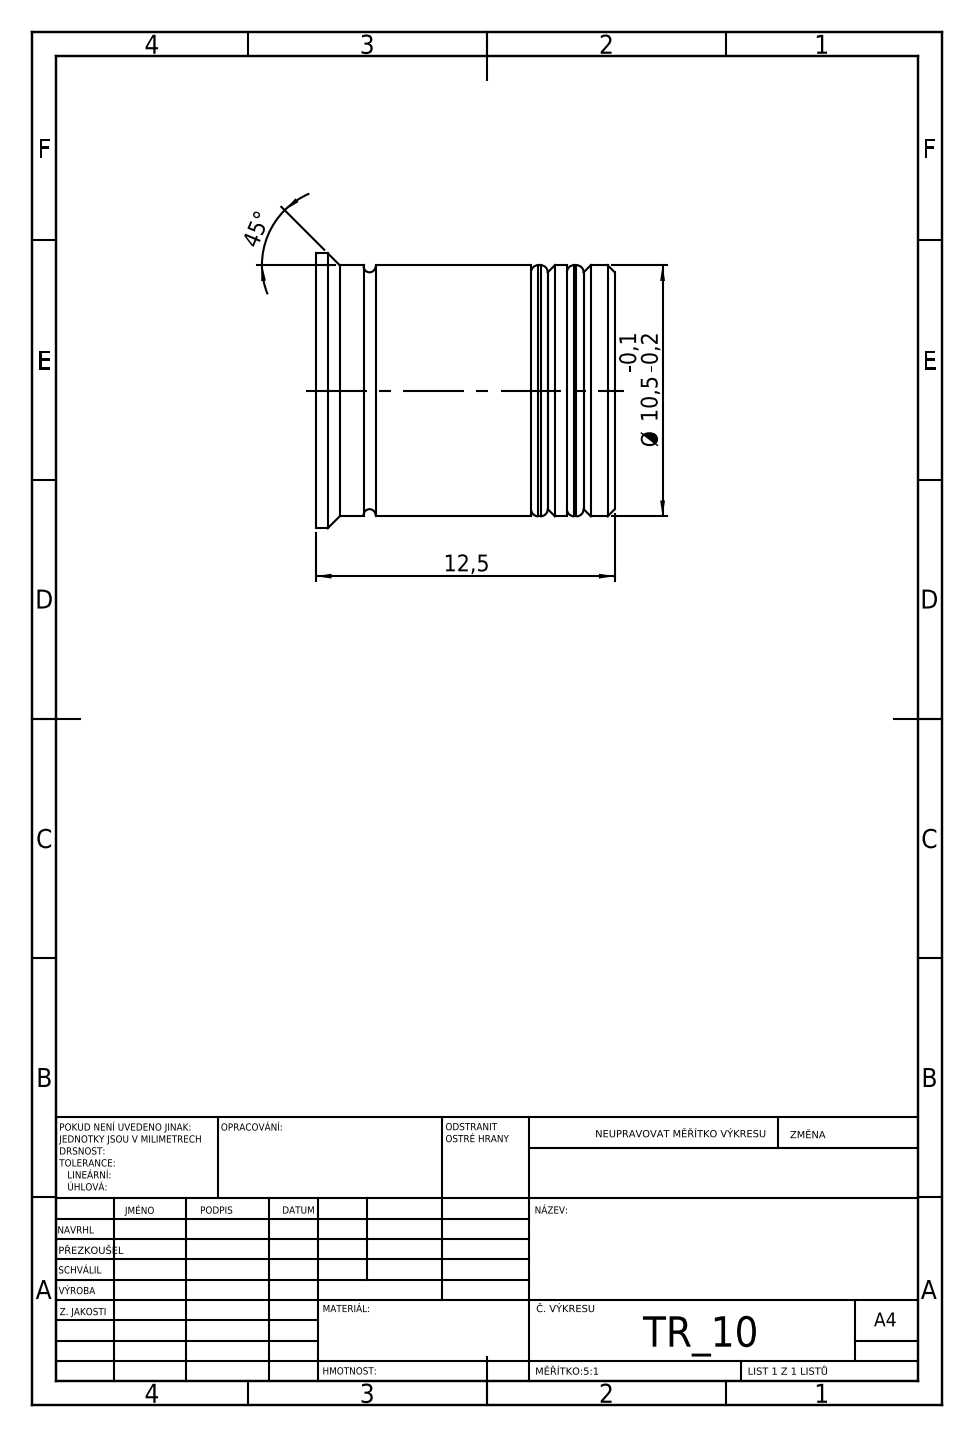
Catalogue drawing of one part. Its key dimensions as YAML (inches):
step_written_by: "SolidWorks 2019 (CONFIG_CONTROL_DESIGN)"
units: inches
bodies: {solids: 3, faces: 74, planar: 29, cylindrical: 25, other: 20}
overall_size: [0.492, 0.453, 0.453]
volume: 0.069
surface_area: 1.694
round_bosses_or_shafts:
  - {diameter: 0.453, count: 1}
  - {diameter: 0.413, count: 1}
  - {diameter: 0.39, count: 1}
  - {diameter: 0.295, count: 1}
face_to_face_distances: [0.059, 0.028, 0.079, 0.087, 0.031, 0.051, 0.11, 0.138, 0.039, 0.343]
